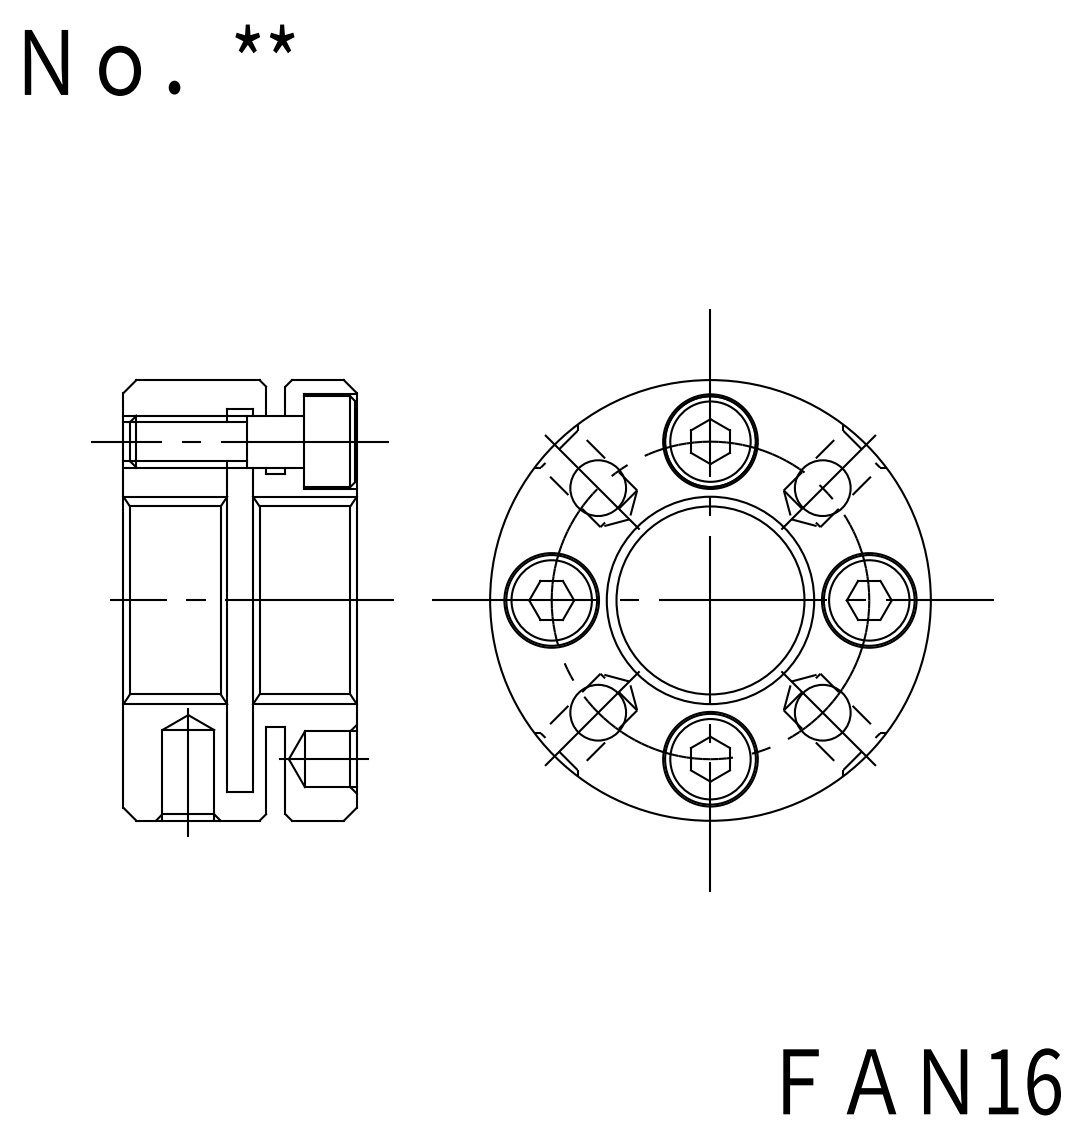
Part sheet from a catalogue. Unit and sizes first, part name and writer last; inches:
Units: inches
Overall size (bounding box): 1.339 × 1.339 × 0.709
Round holes (diameter × count): ⌀0.128 ×4, ⌀0.169 ×4, ⌀0.177 ×4, ⌀0.287 ×4, ⌀0.157 ×2, ⌀0.63 ×1, ⌀1.161 ×1
Round bosses / shafts (diameter × count): ⌀0.276 ×4, ⌀0.157 ×4, ⌀1.339 ×1, ⌀0.768 ×1
Main face-to-face distances: 0.315, 0.394, 0.433, 0.492, 0.059, 0.709, 0.276, 0.217, 0.079, 0.118
Hole centre spacings: 0.369, 0.482, 0.682, 0.891, 0.964, 0.965
Volume: 0.627 in³ · Surface area: 13.77 in²
Bodies: 5 solids, 142 faces (50 planar, 76 cylindrical, 16 other)
Part name (STEP PRODUCT): FKD FAN16; M4X12_default
STEP written by: SolidWorks 2012 (CONFIG_CONTROL_DESIGN)
